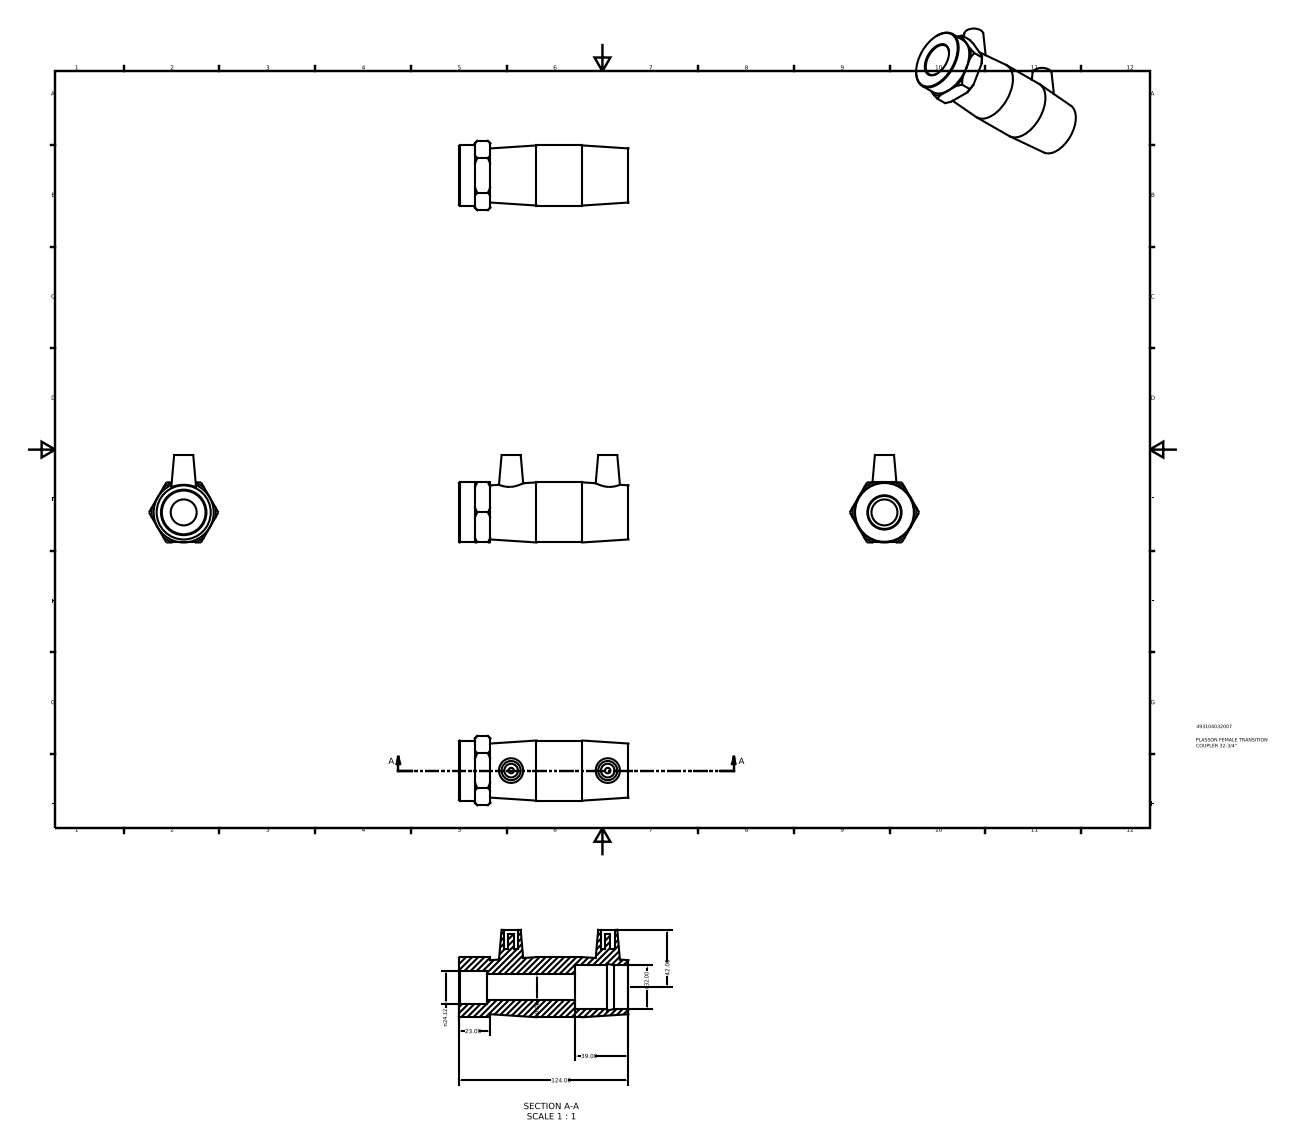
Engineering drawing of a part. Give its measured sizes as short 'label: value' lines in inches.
name: 493104032007
written by: Autodesk Inventor 2015 (AUTOMOTIVE_DESIGN)
unit: in
bodies: 1 solid, 54 faces (24 planar, 10 cylindrical, 20 other)
size: 4.882 × 2.52 × 2
volume: 7.795 in³; area: 49.82 in²
holes: 2× ⌀0.394, 1× ⌀0.748, 1× ⌀0.95, 1× ⌀1.26
bosses: 2× ⌀0.157, 1× ⌀1.732
face distances: 1.732, 3.346, 0.906, 2.441, 4.882, 3.976, 1.535, 0.453, 0.815, 0.091
hole spacings: 2.783
